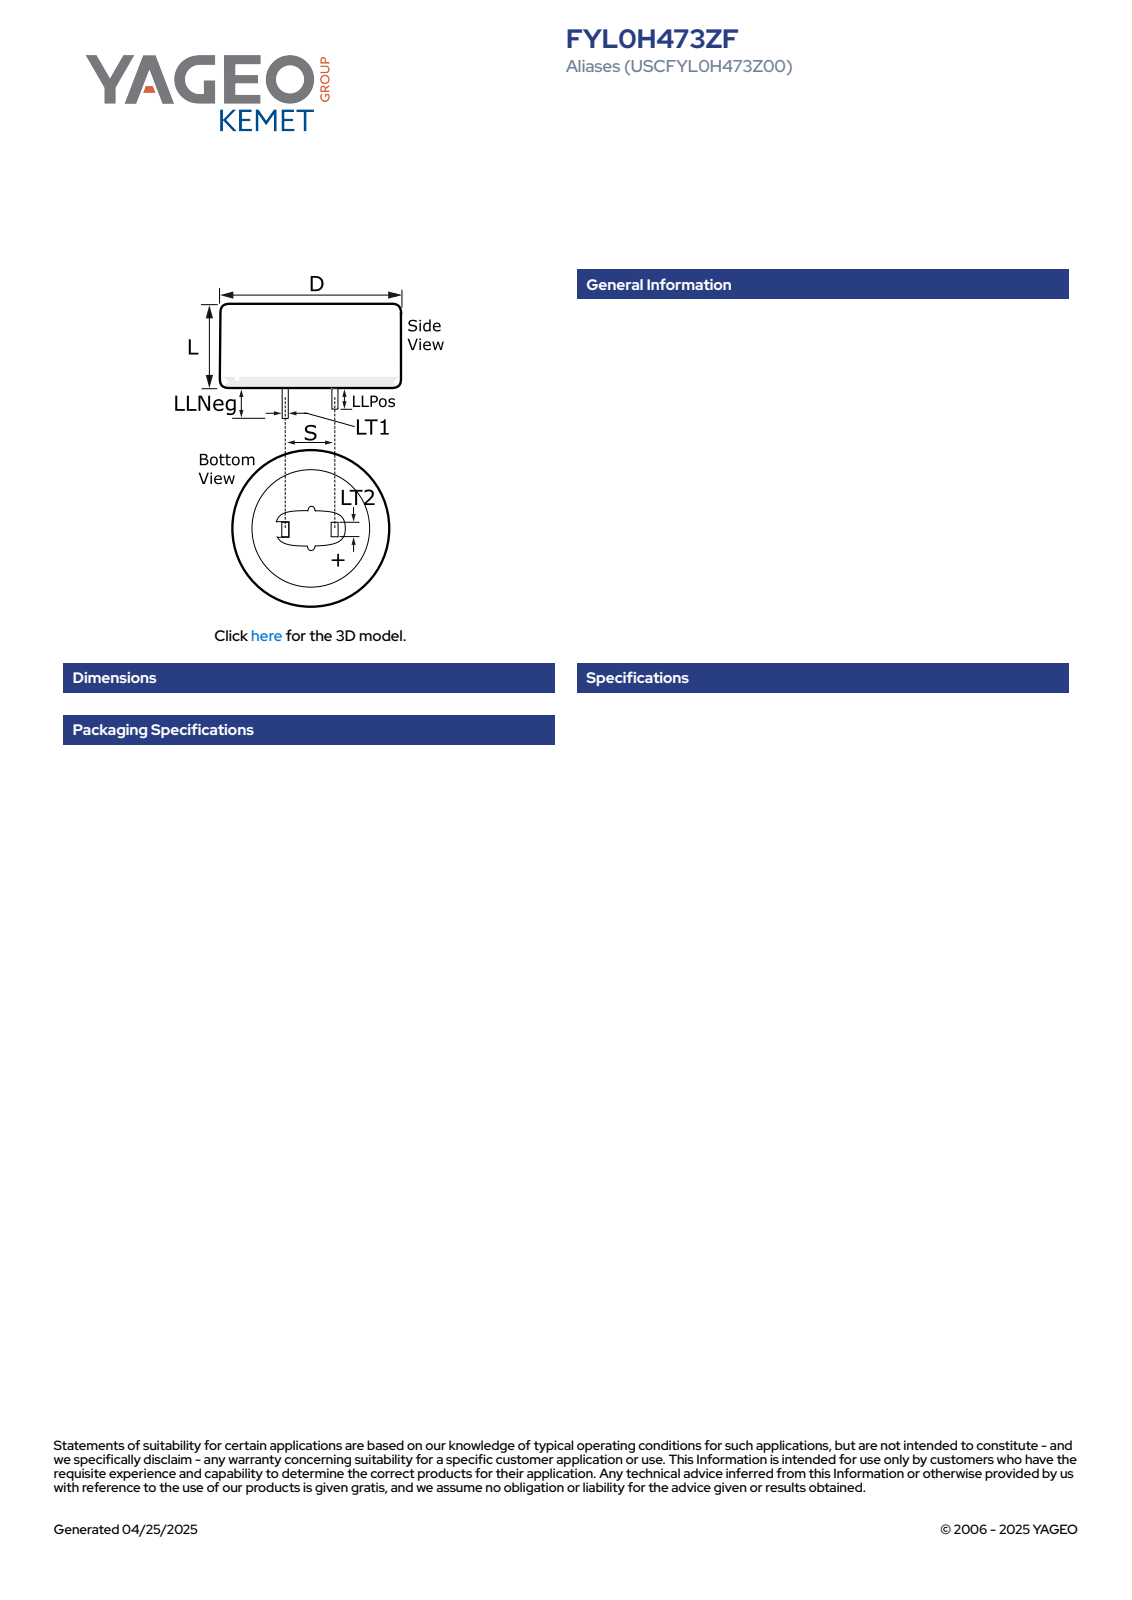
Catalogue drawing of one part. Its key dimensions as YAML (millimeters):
part_name: "CDR_LPLLN_D12.5L5.5S5.08LLNEG3LLPOS2.7LT10.3LT21.3"
step_written_by: "SolidWorks 2014 (AUTOMOTIVE_DESIGN)"
units: millimeters
bodies: {solids: 1, faces: 78, planar: 70, cylindrical: 4, other: 4}
overall_size: [12.5, 12.5, 8.5]
volume: 675
surface_area: 468
round_bosses_or_shafts:
  - {diameter: 12.5, count: 1}
partial_cylinders:
  - {radius: 6.26, count: 1}
face_to_face_distances: [5.5, 5.08, 5.38, 4.78, 1.3, 3, 8.5, 2.7, 8.2, 0.35]
